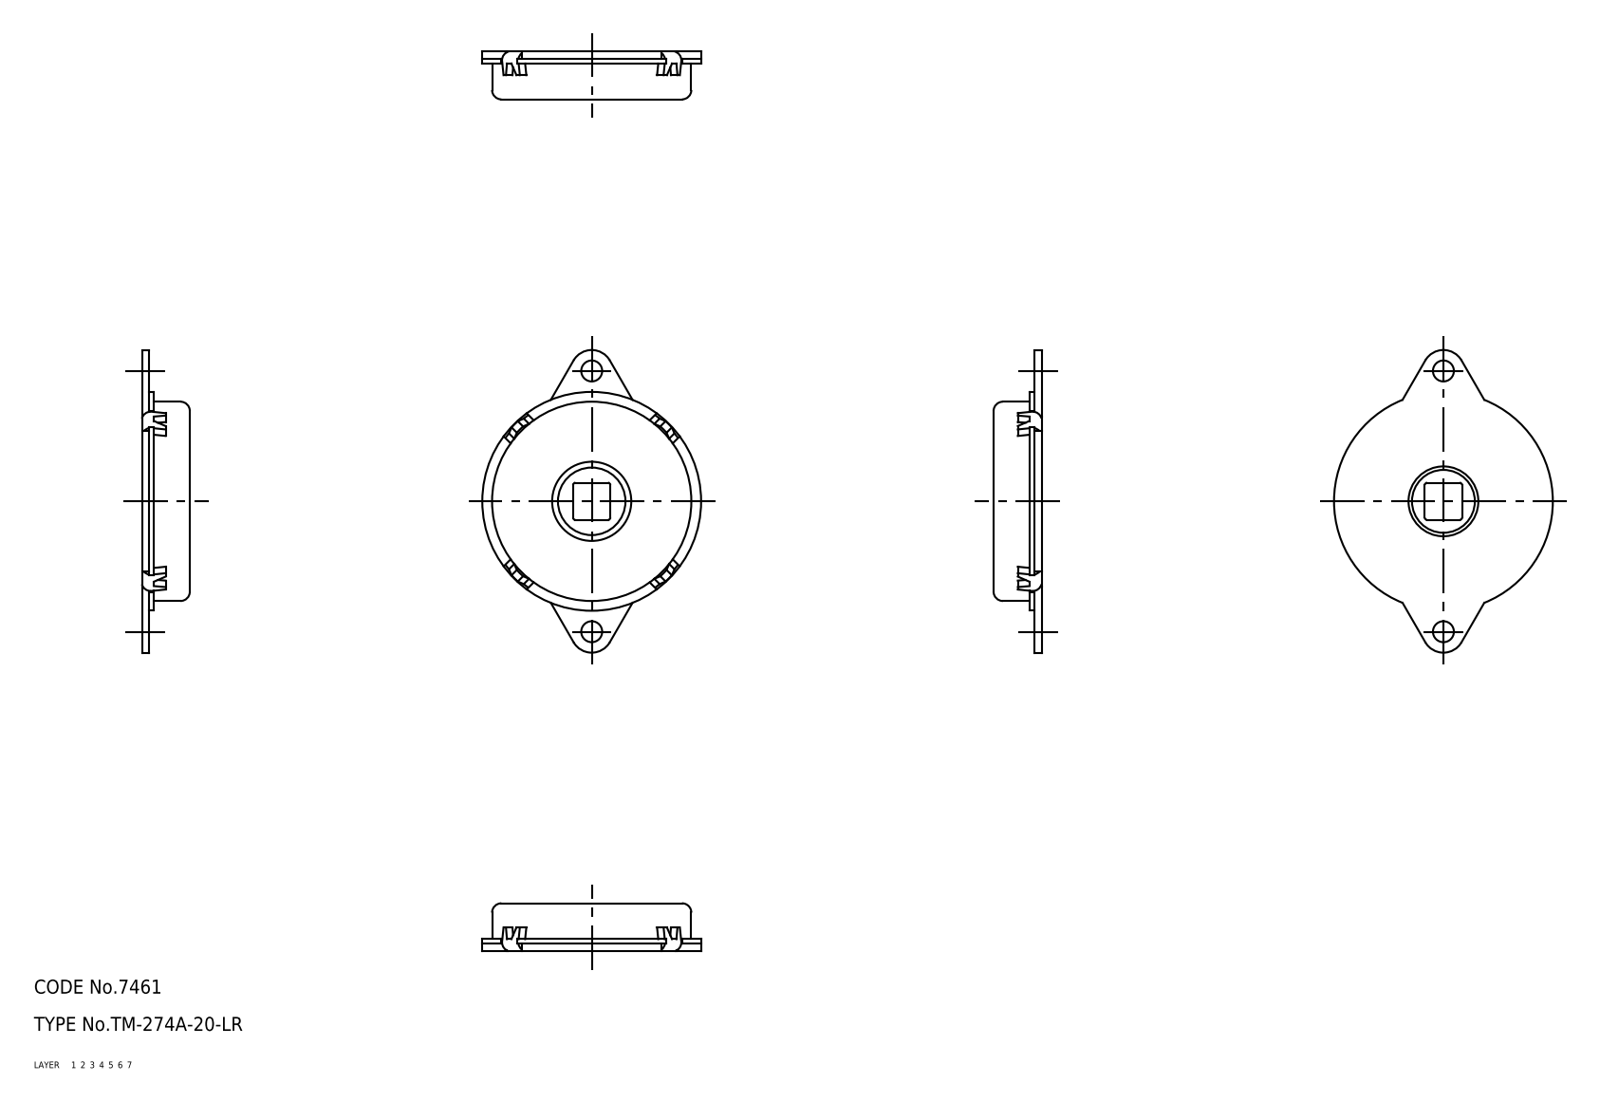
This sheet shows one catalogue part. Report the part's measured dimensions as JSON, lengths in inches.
{"part_name": "inner ring; TM_274A_20_LR_440_36", "step_written_by": "CADfix (AUTOMOTIVE_DESIGN)", "units": "inches", "bodies": {"solids": 2, "faces": 118, "planar": 0, "cylindrical": 0, "other": 118}, "overall_size": [2.559, 1.85, 0.406], "volume_in3": 0.903, "surface_area_in2": 10.46}
